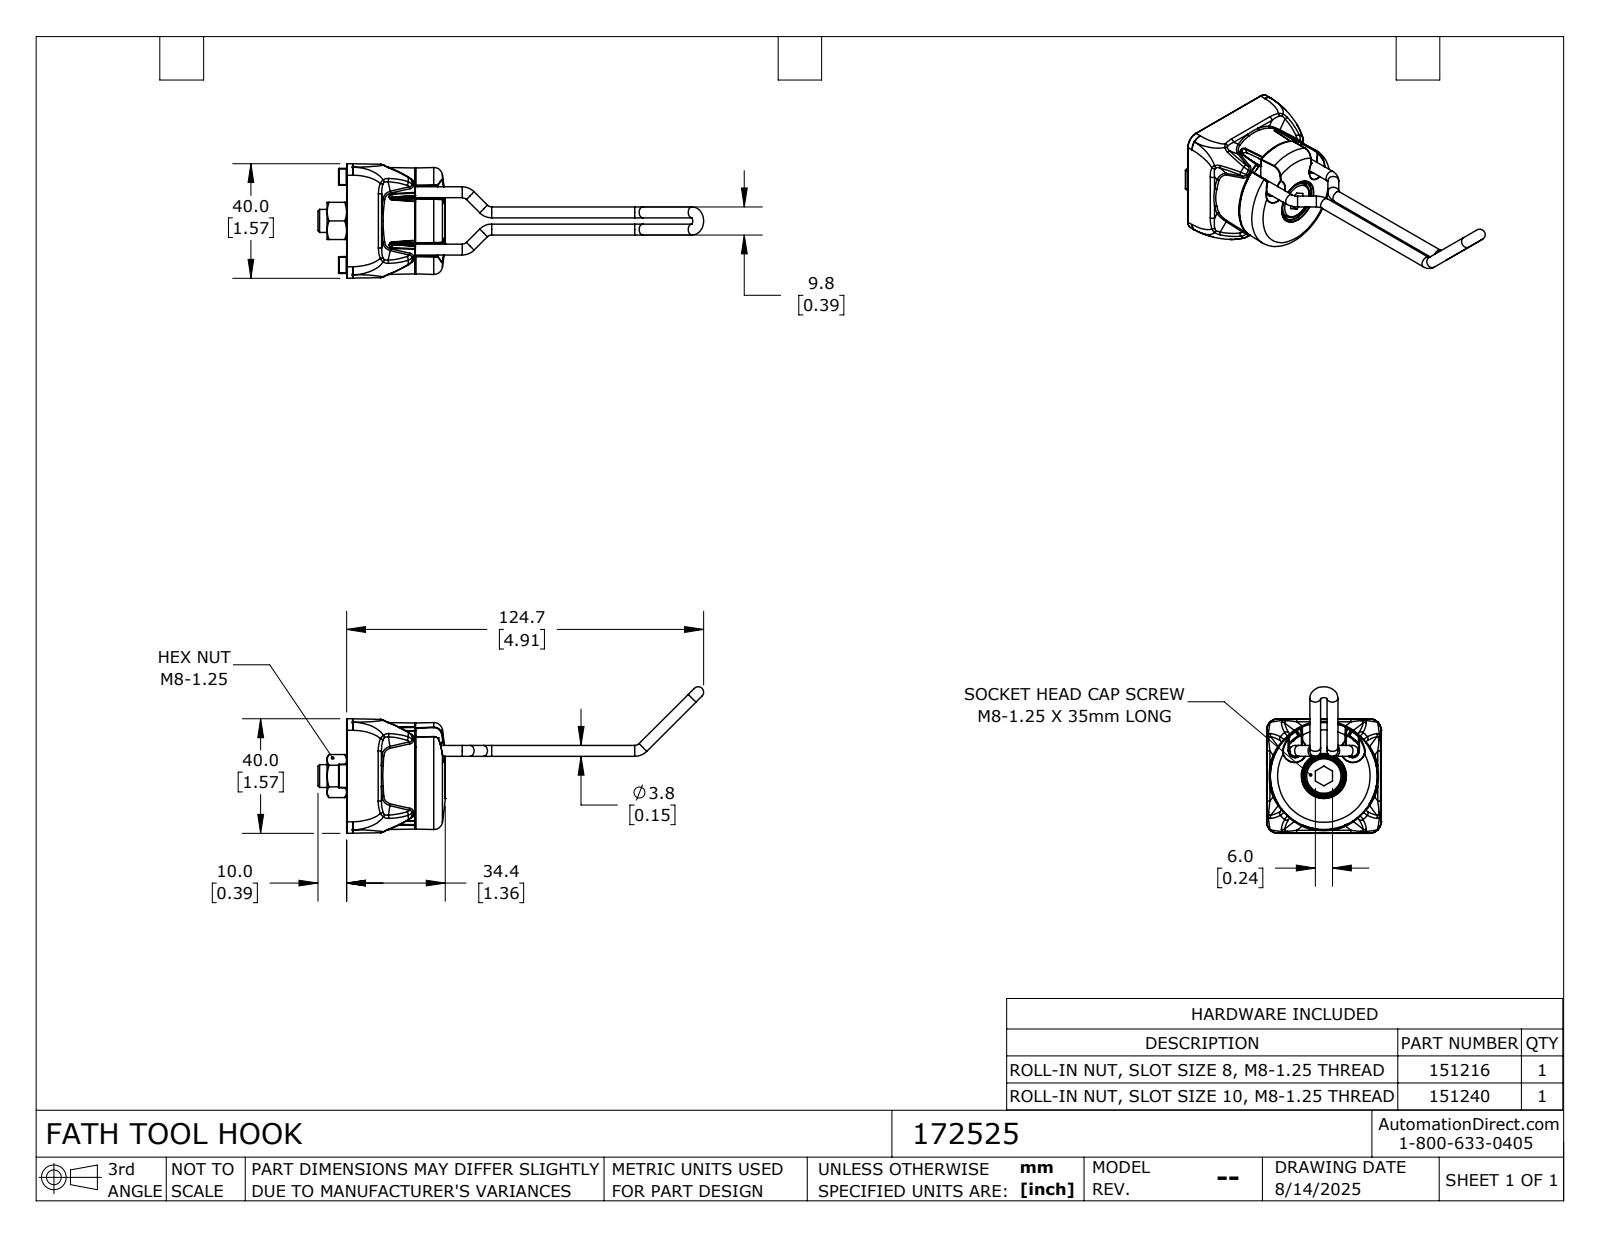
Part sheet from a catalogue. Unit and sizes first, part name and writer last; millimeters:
Units: millimetres
Overall size (bounding box): 134.69 × 51.16 × 40
Round holes (diameter × count): ⌀6.8 ×1, ⌀8 ×1, ⌀13.01 ×1
Round bosses / shafts (diameter × count): ⌀3.8 ×12, ⌀13 ×1
Partial cylindrical surfaces — rounded edges, fillets, slot ends (radius × count): R0.2 ×142, R0.5 ×22, R1 ×8, R4 ×8, R1.2 ×4, R2.15 ×2, R16.5 ×1
Main face-to-face distances: 13, 6, 30.8, 11, 13.3, 17, 8, 10.7, 24, 9.2
Volume: 40 719 mm³ · Surface area: 22 487 mm²
Bodies: 7 solids, 1297 faces (230 planar, 308 cylindrical, 759 other)
Part name (STEP PRODUCT): 172525
STEP written by: SolidWorks 2024 (CONFIG_CONTROL_DESIGN)
